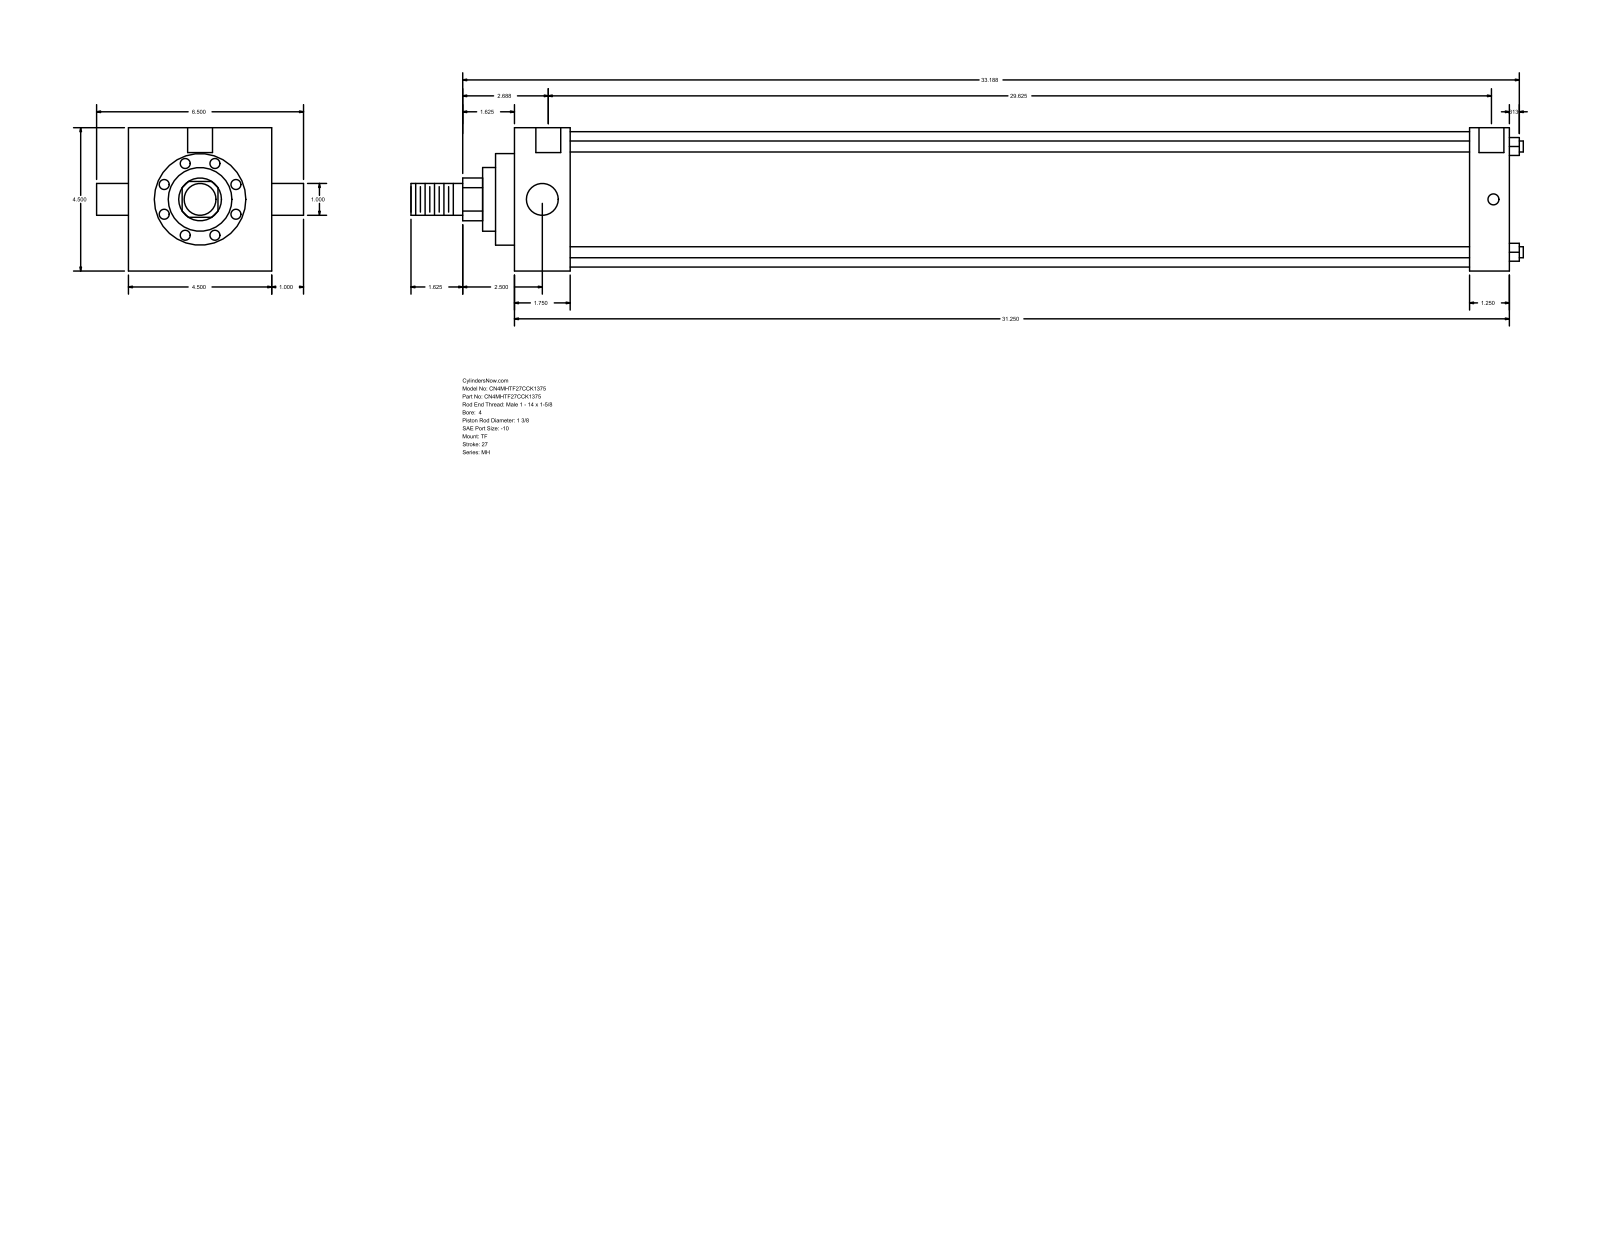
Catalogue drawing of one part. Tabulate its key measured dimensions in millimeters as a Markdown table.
| quantity | value |
| --- | --- |
| part name | MH_TF__0400_1.375 |
| STEP written by | GSSL Pune (CONFIG_CONTROL_DESIGN) |
| units | millimeters |
| bodies | 0 solids, 86 faces (61 planar, 25 cylindrical, 0 other) |
| overall size | 887.41 × 165.1 × 114.3 |
| round holes (diameter × count) | 8.73 × 3, 19.84 × 2 |
| round bosses / shafts (diameter × count) | 8.76 × 4, 25.4 × 2, 107.95 × 1, 73.03 × 1, 50.8 × 1, 34.92 × 1 |
| partial cylindrical surfaces (radius × count) | 17.06 × 1 |
| main face-to-face distances | 114.3, 793.75, 44.45, 749.3, 762, 717.55, 31.75, 15.08, 59.53, 777.08 |
| hole center spacings | 1.59, 754.07, 752.48, 755.66 |
